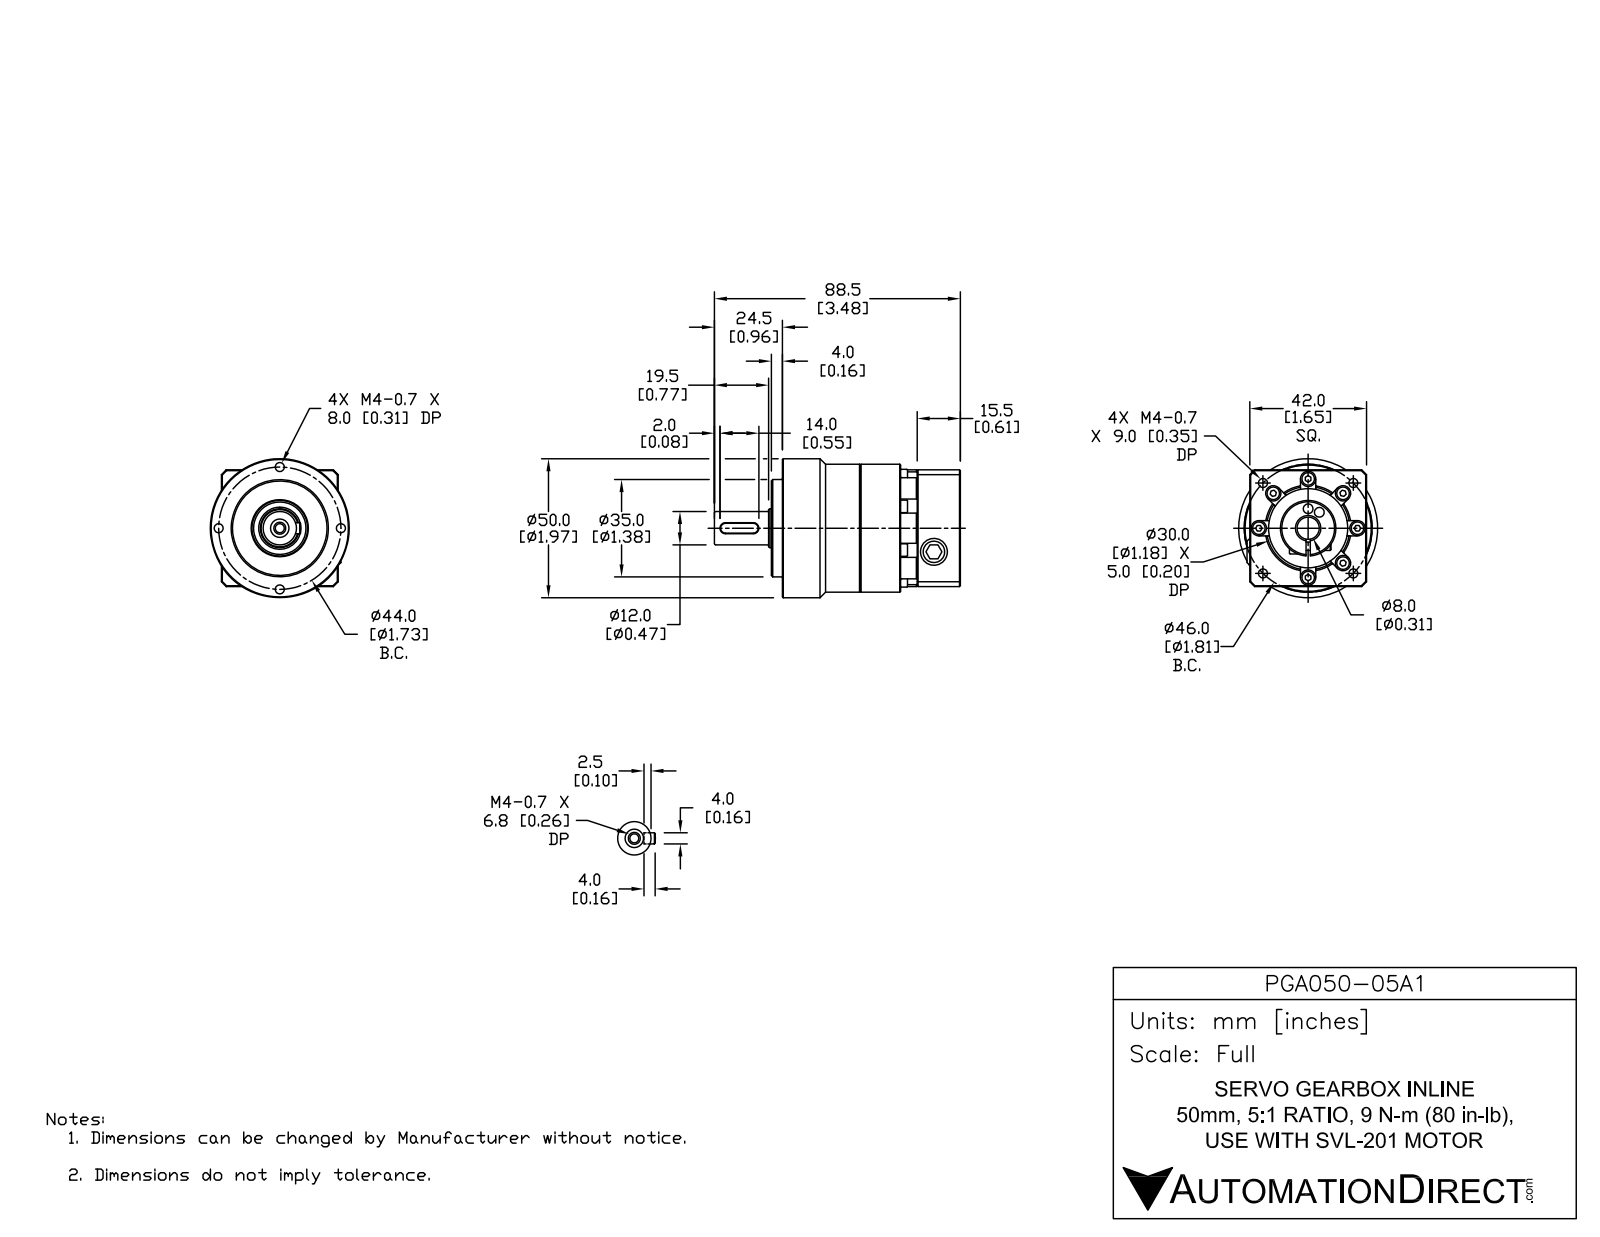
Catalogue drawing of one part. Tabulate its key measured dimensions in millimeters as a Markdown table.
| quantity | value |
| --- | --- |
| part name | PGA050-05A1 |
| STEP written by | SolidWorks 2014 (AUTOMOTIVE_DESIGN) |
| units | millimeters |
| bodies | 1 solid, 570 faces (229 planar, 159 cylindrical, 182 other) |
| overall size | 88.5 × 50 × 50 |
| volume | 104 700 mm³ |
| surface area | 22 480 mm² |
| round holes (diameter × count) | 3.3 × 9, 2.8 × 7, 5.5 × 7, 3.5 × 3, 4.3 × 1, 8 × 1, 20 × 1, 28.5 × 1 |
| round bosses / shafts (diameter × count) | 4.5 × 15, 2.5 × 7, 50 × 1, 46 × 1, 35 × 1, 14 × 1, 12 × 1, 5.5 × 1 |
| partial cylindrical surfaces (radius × count) | 2.7 × 8, 2 × 2, 1.2 × 1, 3.3 × 1, 4 × 1, 15 × 1, 21 × 1, 28.5 × 1 |
| main face-to-face distances | 42, 48.5, 15.5, 64, 4, 68, 52.5, 5, 10.5, 6 |
| hole center spacings | 16.3, 17.2, 28.3, 37.7, 41.6, 17.8, 13.6, 15.7 |
